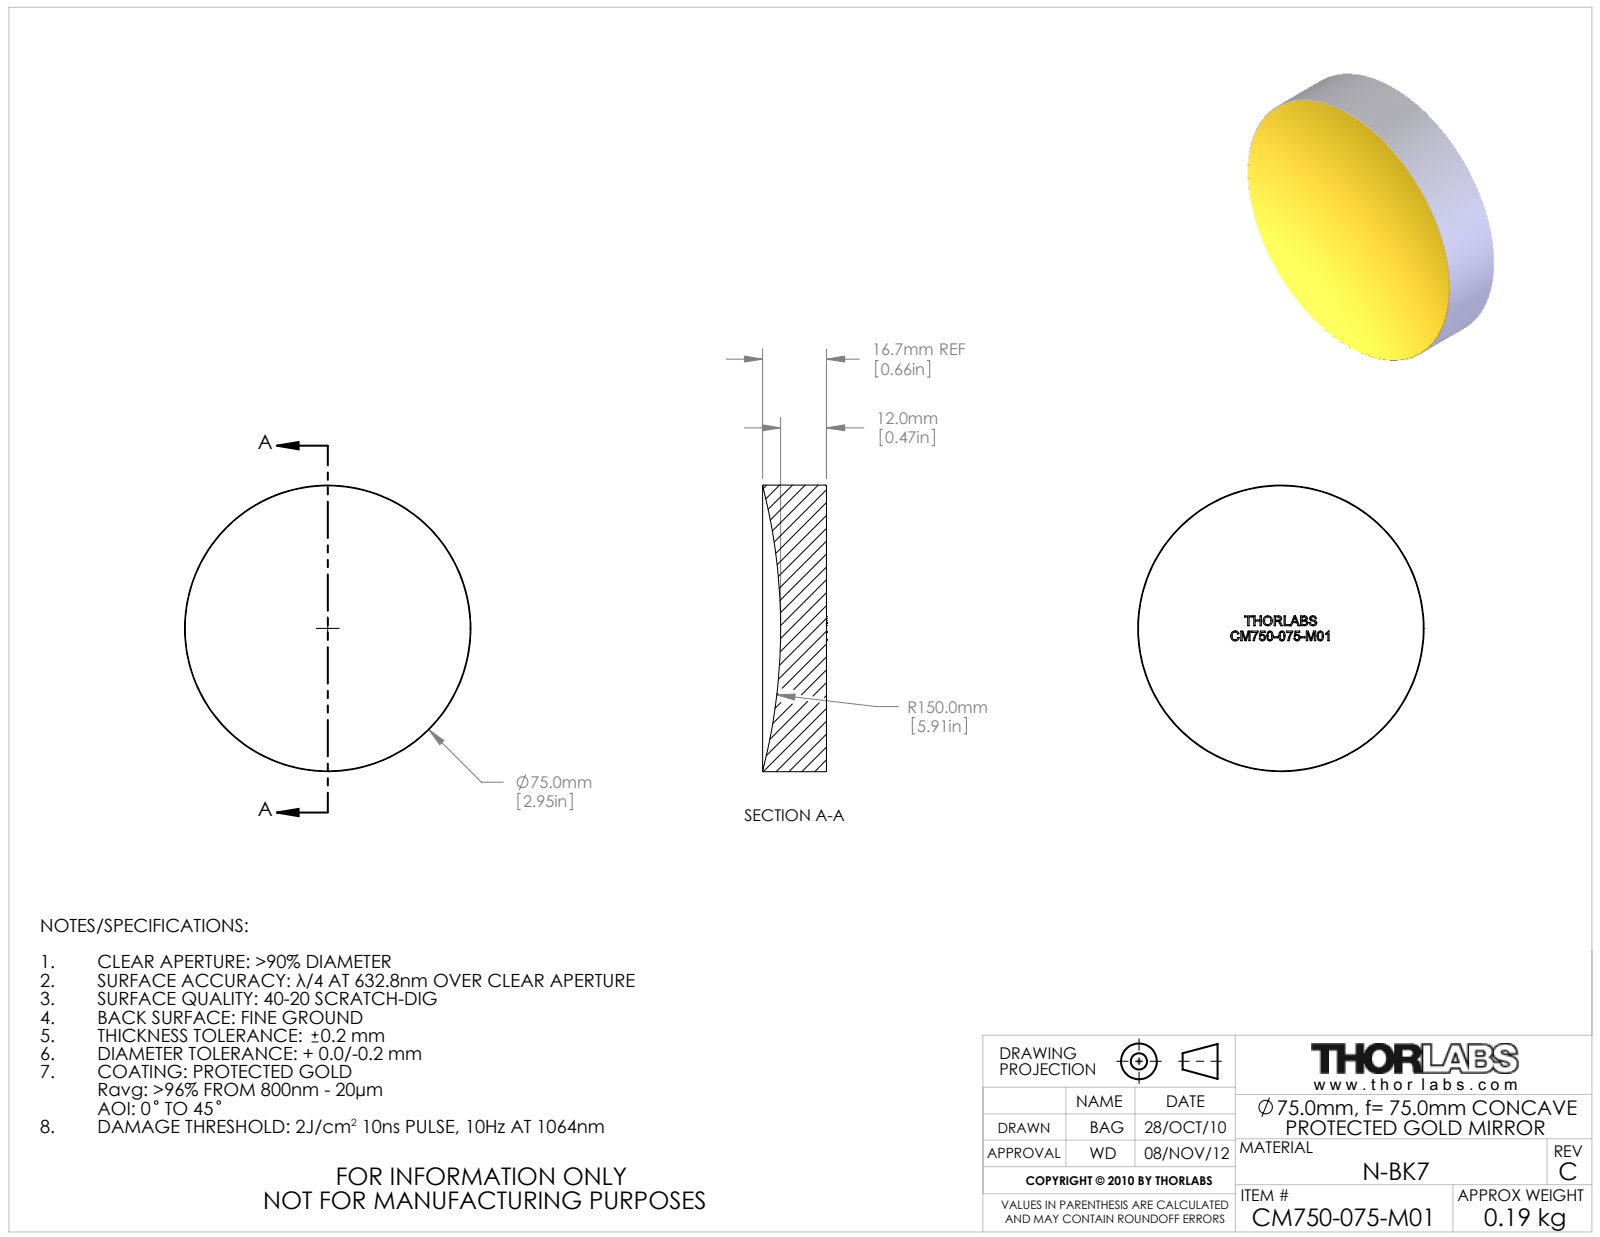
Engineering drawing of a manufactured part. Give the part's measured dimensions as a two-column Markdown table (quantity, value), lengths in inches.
| quantity | value |
| --- | --- |
| part name | 17590-E0W |
| STEP written by | SolidWorks 2009 (AUTOMOTIVE_DESIGN) |
| units | inches |
| bodies | 1 solid, 272 faces (154 planar, 2 cylindrical, 116 other) |
| overall size | 2.953 × 2.953 × 0.658 |
| volume | 3.873 in³ |
| surface area | 19.83 in² |
| round bosses / shafts (diameter × count) | 2.953 × 1 |
| main face-to-face distances | 0.014, 0.101, 0.015, 0.013, 0.675, 0.069, 0.083, 0.157, 0.126, 0.097 |
